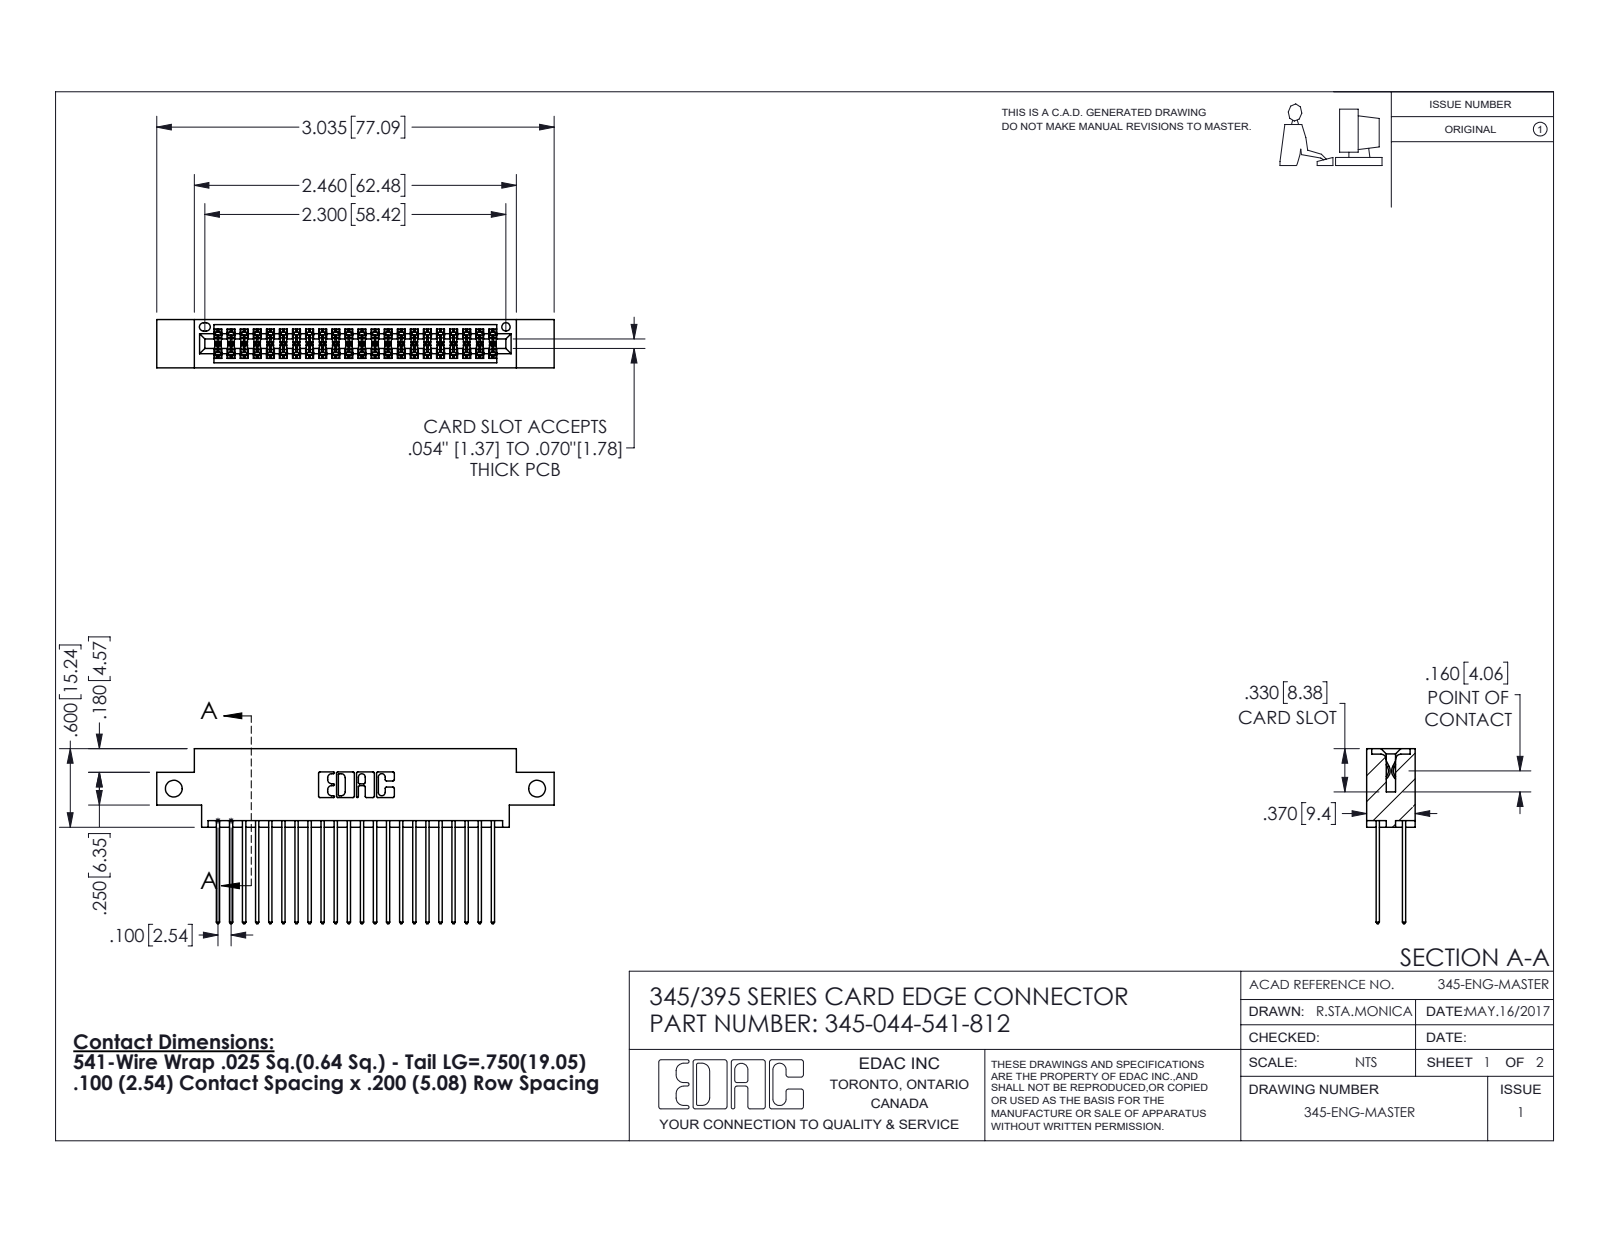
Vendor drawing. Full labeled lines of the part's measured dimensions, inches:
Part name (STEP PRODUCT): 345-044-541-812; 345-292-001_345-293-141; 345 Part_0.170 Offset - Side Mount
STEP written by: SolidWorks 2016 (CONFIG_CONTROL_DESIGN)
Units: inches
Bodies: 45 solids, 2330 faces (1536 planar, 794 cylindrical, 0 other)
Overall size (bounding box): 3.035 × 1.337 × 0.37
Volume: 0.449 in³ · Surface area: 18.1 in²
Round holes (diameter × count): ⌀0.128 ×2, ⌀0.064 ×1
Partial cylindrical surfaces — rounded edges, fillets, slot ends (radius × count): R0.006 ×66, R0.01 ×44, R0.01 ×22, R0.007 ×6, R0.031 ×6, R0.026 ×3, R0.014 ×2, R0.019 ×2
Main face-to-face distances: 0.298, 0.072, 0.2, 0.098, 0.272, 0.025, 0.37, 0.225, 0.175, 0.15
Hole centre spacings: 2.775
